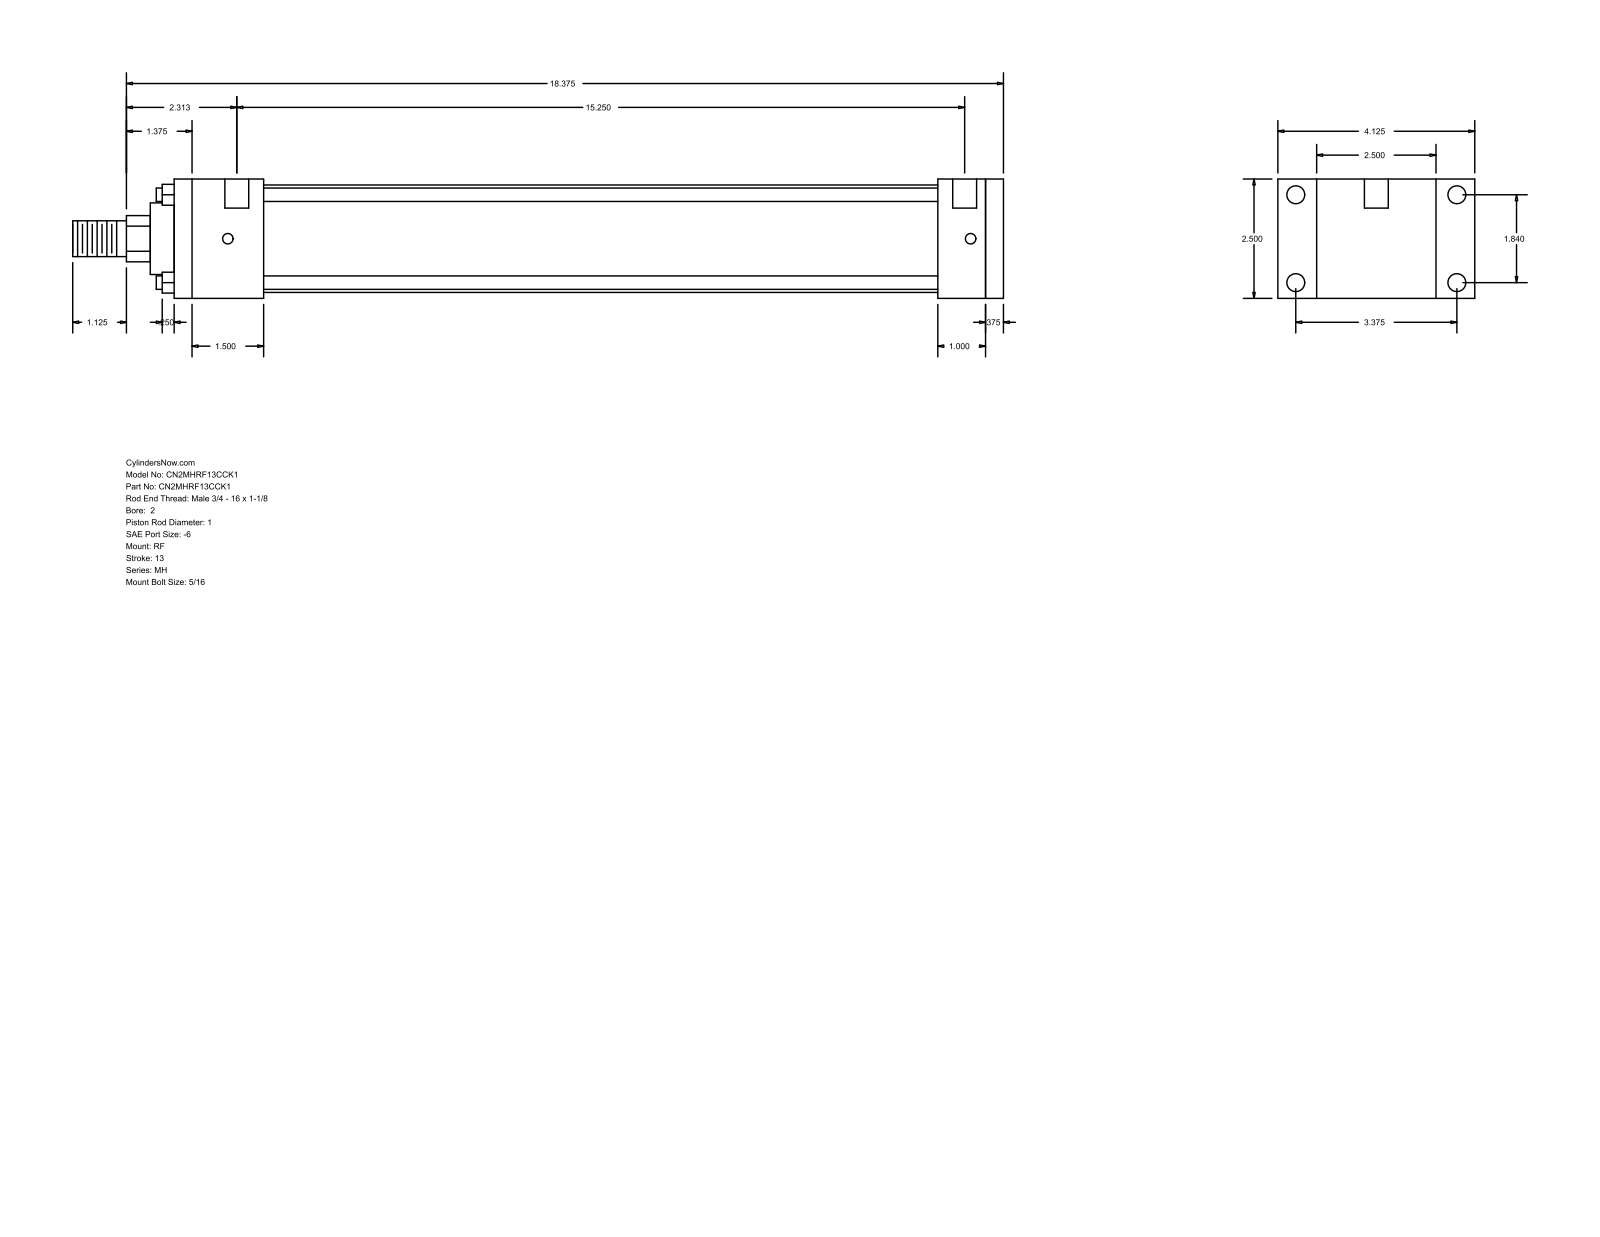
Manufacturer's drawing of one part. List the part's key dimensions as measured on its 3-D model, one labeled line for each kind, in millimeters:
Part name (STEP PRODUCT): MH_RF__0200_1
STEP written by: GSSL Pune (CONFIG_CONTROL_DESIGN)
Units: millimetres
Bodies: 0 solids, 92 faces (64 planar, 28 cylindrical, 0 other)
Overall size (bounding box): 495.3 × 104.78 × 63.5
Round holes (diameter × count): ⌀5.56 ×4, ⌀9.53 ×4, ⌀12.7 ×2
Round bosses / shafts (diameter × count): ⌀7.14 ×4, ⌀57.15 ×1, ⌀38.1 ×1, ⌀25.4 ×1, ⌀19.05 ×1
Partial cylindrical surfaces — rounded edges, fillets, slot ends (radius × count): R12.29 ×1
Main face-to-face distances: 63.5, 441.33, 431.8, 9.53, 20.64, 25.4, 47.63, 406.4, 358.77, 384.17
Hole centre spacings: 46.74, 85.72, 97.63, 395.28, 3.17, 4.76, 387.35, 390.52
